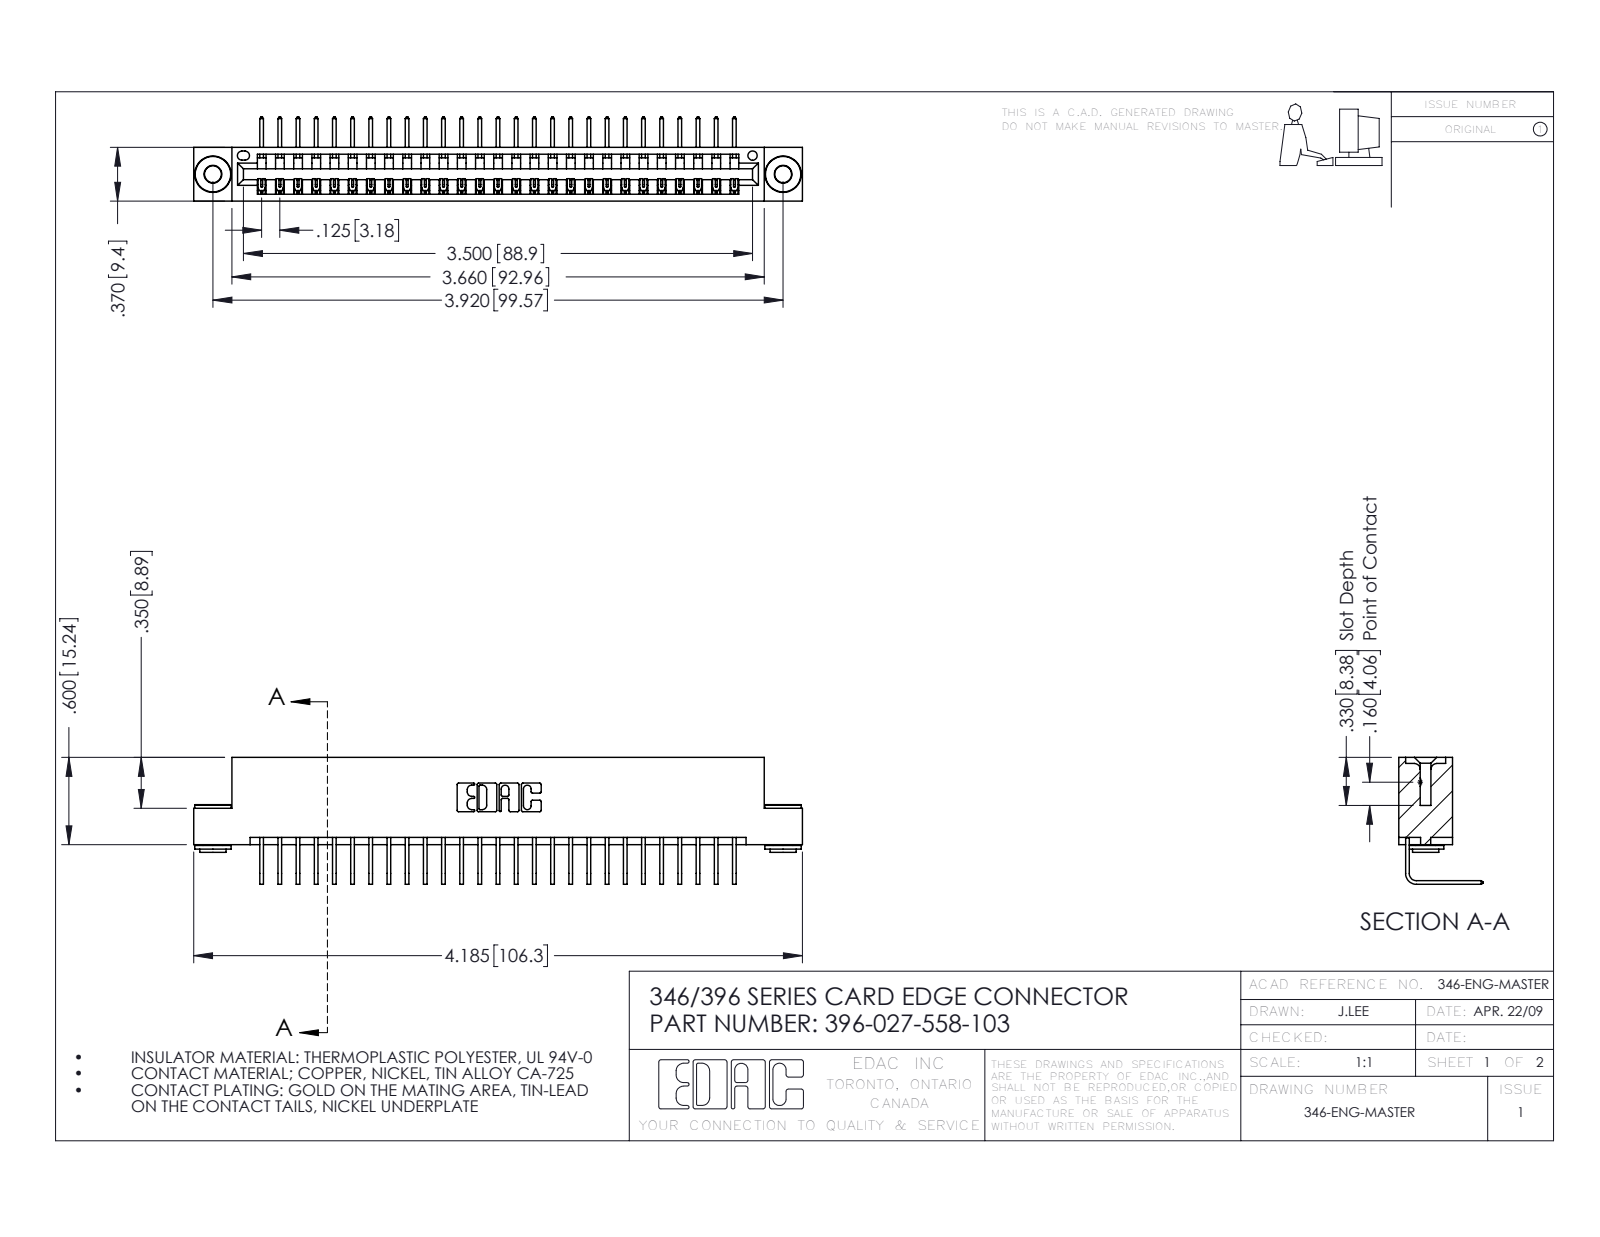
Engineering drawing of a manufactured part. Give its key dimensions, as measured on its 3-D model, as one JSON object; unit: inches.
{"part_name": "396-027-558-103; 346 Part_Flush Mounting Lugs - 0.156 Dia-TH; 345-292-001_558 Tail - 2; 345-250-002_345-250-002-102", "step_written_by": "SolidWorks 2016 (CONFIG_CONTROL_DESIGN)", "units": "inches", "bodies": {"solids": 30, "faces": 1780, "planar": 1220, "cylindrical": 552, "other": 8}, "overall_size": [4.185, 0.873, 0.58], "volume_in3": 0.621, "surface_area_in2": 20.64, "round_holes": [[0.116, 2], [0.156, 2], [0.064, 1]], "round_bosses_or_shafts": [[0.25, 2], [0.18, 2], [0.136, 2]], "partial_cylinders_radius": [[0.006, 54], [0.01, 22], [0.007, 6], [0.031, 6], [0.026, 3], [0.031, 2], [0.04, 2], [0.014, 1]], "face_to_face_distances": [0.322, 0.048, 0.37, 0.25, 0.025, 0.298, 0.072, 0.148, 0.222, 0.1], "hole_center_spacings": [0.246, 3.712, 3.92]}
